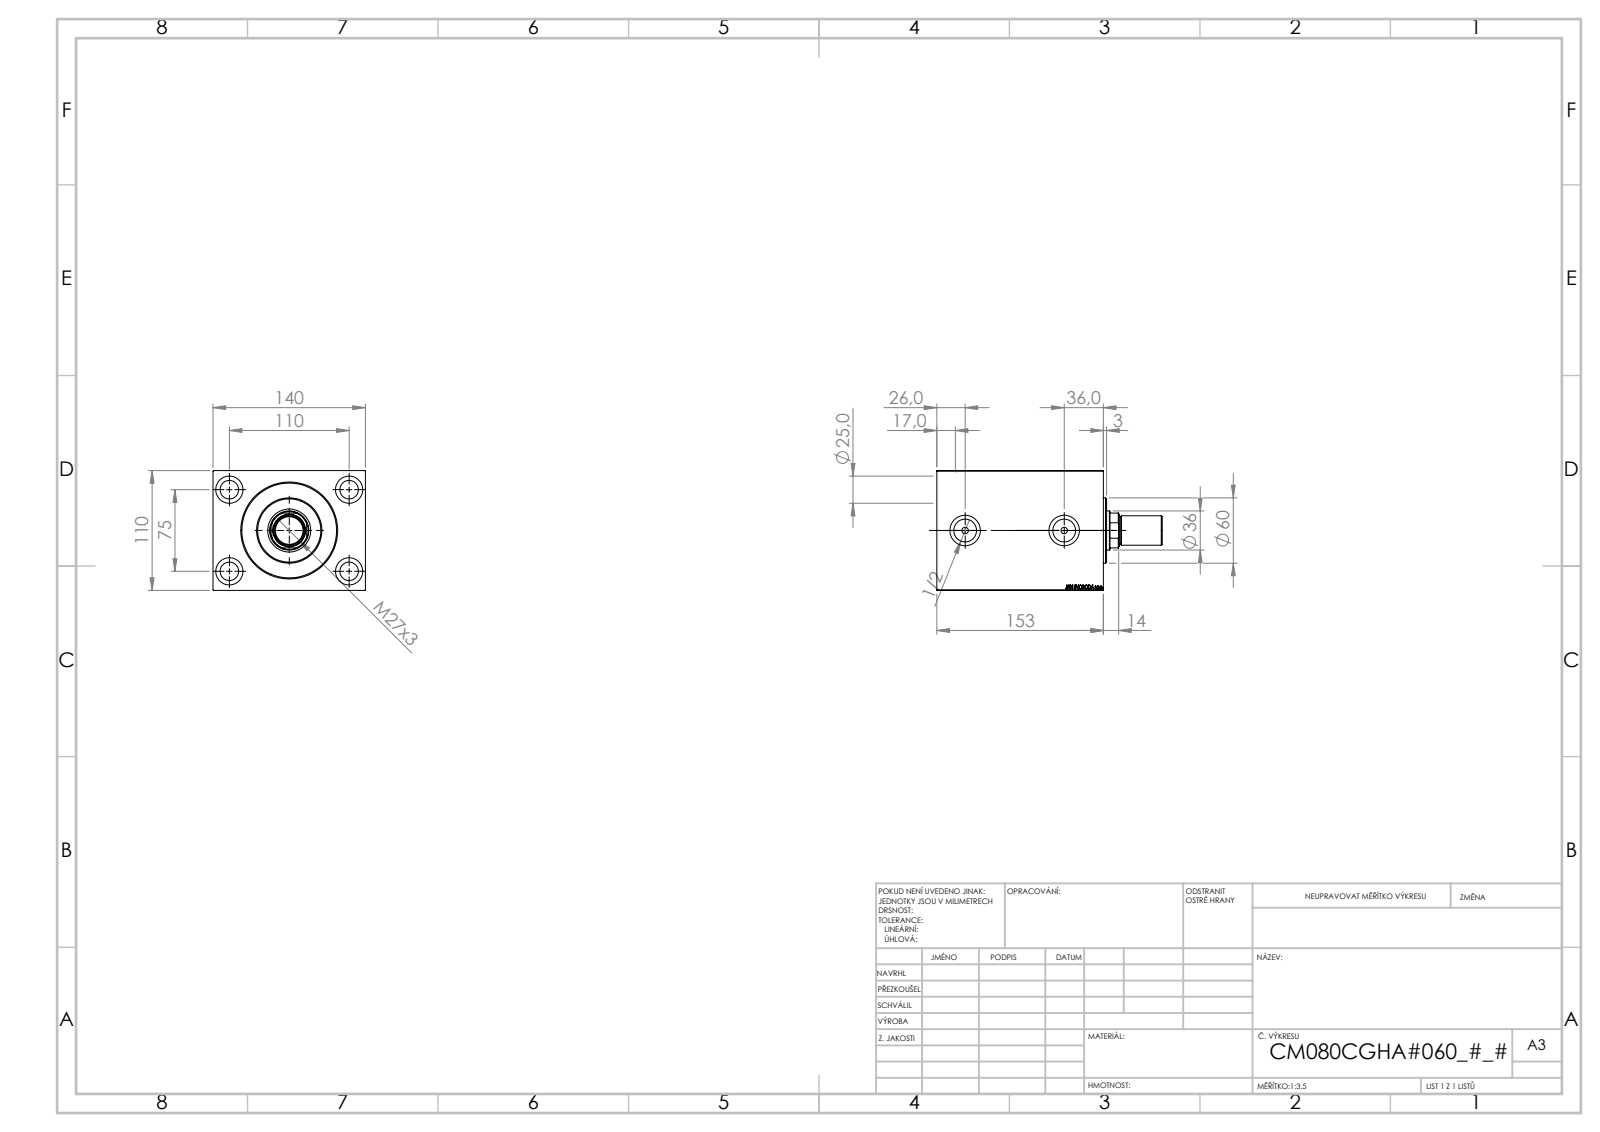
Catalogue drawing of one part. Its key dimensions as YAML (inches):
part_name: "V450CM_C_Body; V450CM_VC_B; V450CM_MALE_METRIC; V450CM_C_VCP"
step_written_by: "SolidWorks 2019 (CONFIG_CONTROL_DESIGN)"
units: inches
bodies: {solids: 4, faces: 879, planar: 413, cylindrical: 66, other: 400}
overall_size: [8.15, 5.512, 4.331]
volume: 119.2
surface_area: 364.1
round_holes:
  - {diameter: 0.669, count: 4}
  - {diameter: 0.984, count: 4}
  - {diameter: 0.236, count: 2}
  - {diameter: 0.825, count: 2}
  - {diameter: 1.102, count: 2}
  - {diameter: 1.004, count: 1}
  - {diameter: 1.417, count: 1}
  - {diameter: 1.555, count: 1}
  - {diameter: 3.15, count: 1}
  - {diameter: 3.228, count: 1}
  - {diameter: 3.425, count: 1}
round_bosses_or_shafts:
  - {diameter: 2.362, count: 1}
  - {diameter: 1.063, count: 1}
  - {diameter: 0.984, count: 1}
partial_cylinders:
  - {radius: 0.689, count: 1}
face_to_face_distances: [4.331, 5.512, 6.024, 5.197, 0.827, 0.551, 5.472, 4.646, 2.913, 2.362]
hole_center_spacings: [2.621, 2.953, 4.331, 5.242, 3.583]
